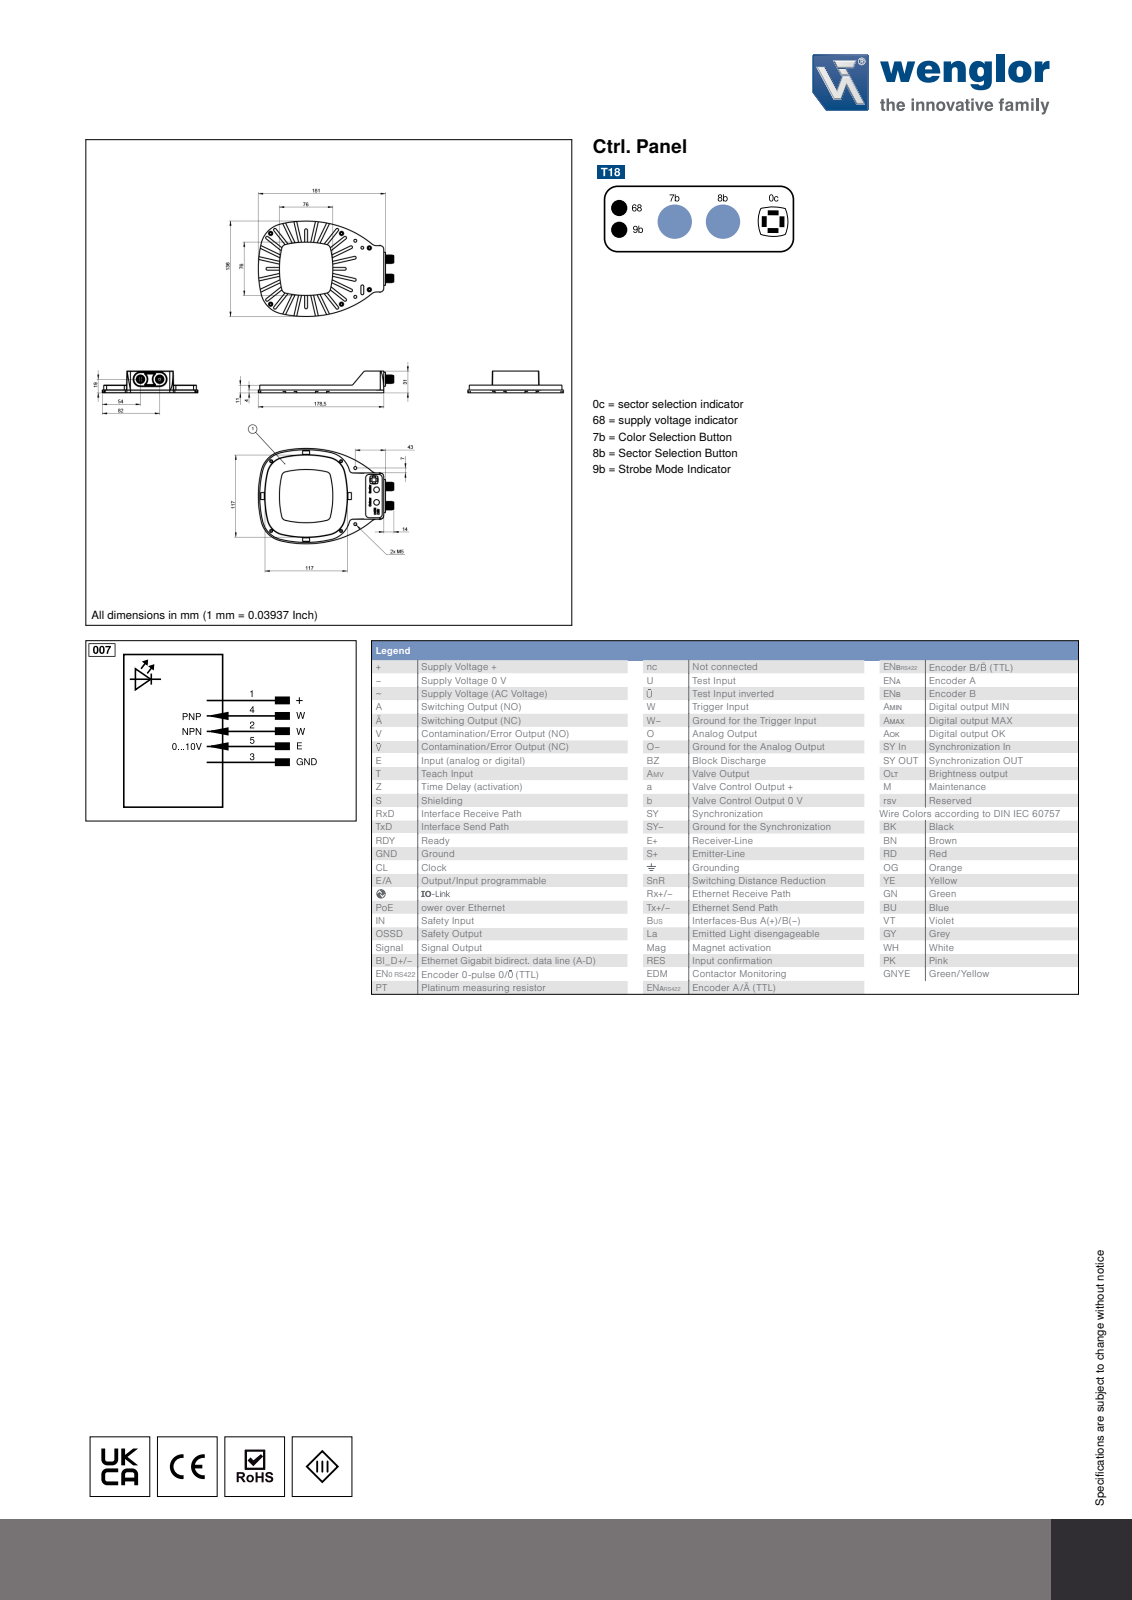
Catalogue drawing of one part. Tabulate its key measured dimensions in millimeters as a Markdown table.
| quantity | value |
| --- | --- |
| part name | OPT2426 and OPT2427 |
| STEP written by | SolidWorks 2021 (CONFIG_CONTROL_DESIGN) |
| units | millimeters |
| bodies | 1 solid, 1948 faces (422 planar, 569 cylindrical, 957 other) |
| overall size | 256.8 × 197 × 31 |
| volume | 274 500 mm³ |
| surface area | 70 840 mm² |
| round holes (diameter × count) | 6 × 6, 3 × 4, 4.2 × 4, 4.2 × 2, 8.3 × 2, 4 × 1, 9.4 × 1, 9.8 × 1 |
| round bosses / shafts (diameter × count) | 0.8 × 8, 1 × 5, 12.2 × 2, 10.7 × 2 |
| partial cylindrical surfaces (radius × count) | 0.3 × 334, 0.5 × 27, 0.2 × 16, 2 × 16, 5 × 6, 32.7 × 4, 58.1 × 4, 58.2 × 4 |
| main face-to-face distances | 11, 2, 9, 4, 7, 26.5, 19.5, 30.5, 28.5, 0.5 |
| hole center spacings | 143.2, 144, 1, 25.6, 42.5, 42.5, 66.5, 66.6 |
